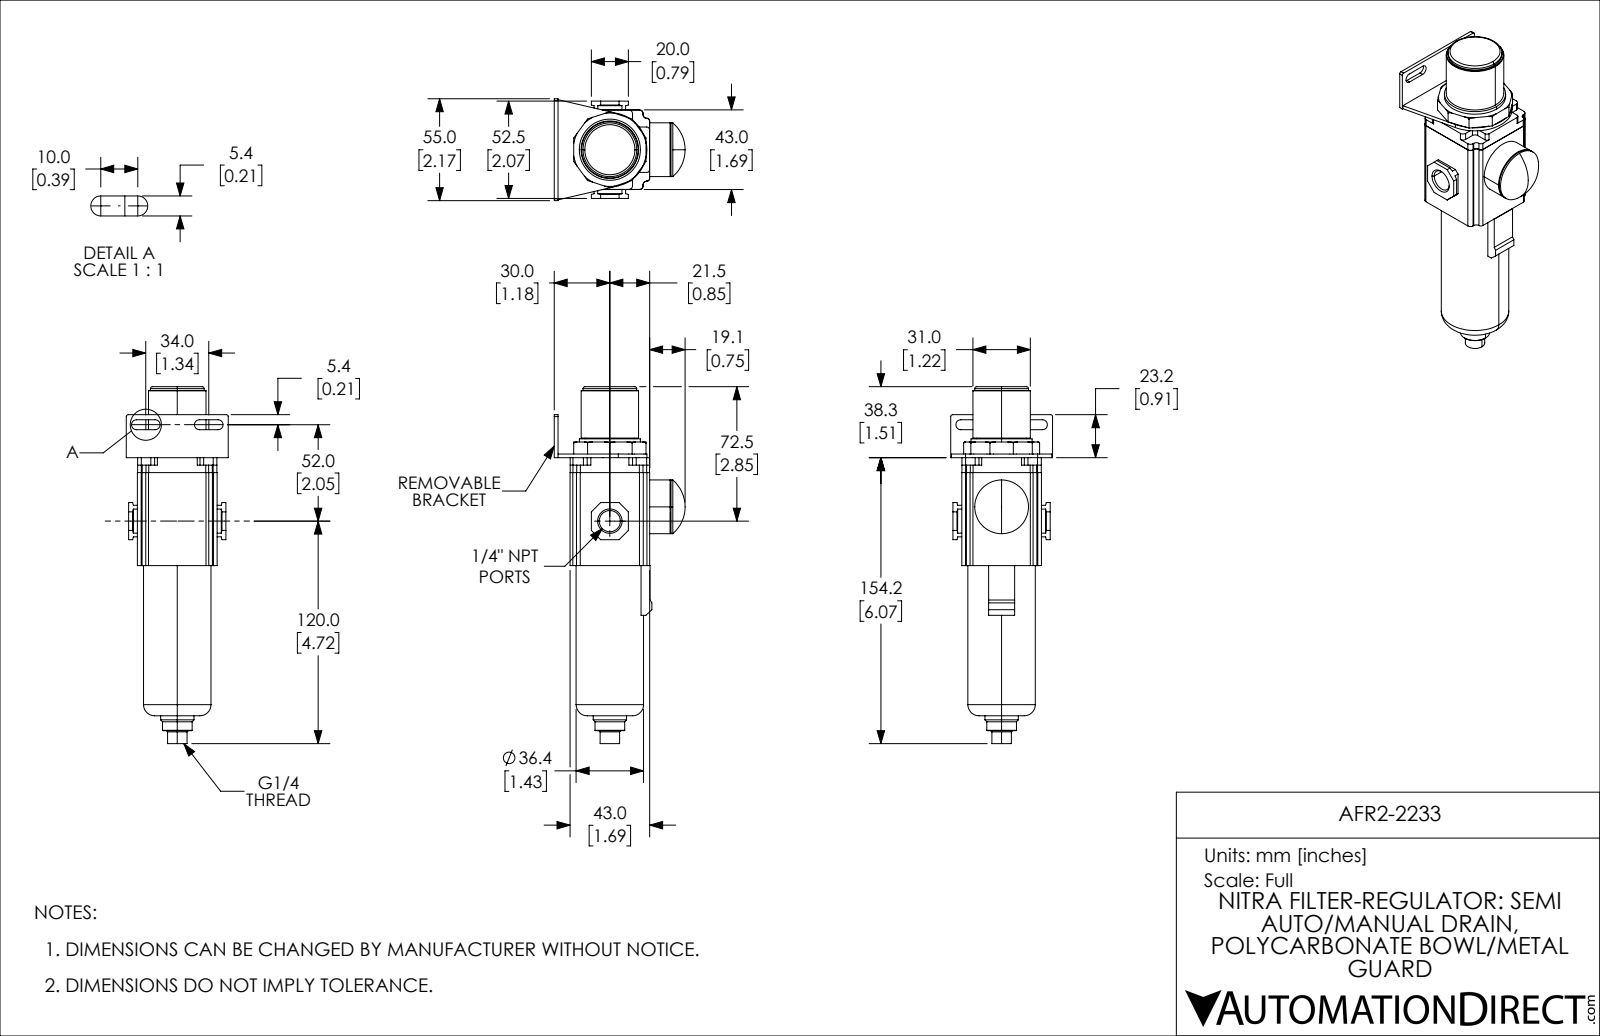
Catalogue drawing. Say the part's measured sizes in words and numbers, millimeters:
The part is named "AFR2-2233". Its 3-D file was written by "SolidWorks 2019 (CONFIG_CONTROL_DESIGN)". It is 1 solid with 220 faces: 119 planar, 69 cylindrical and 32 other. Overall it measures 192.5 by 70.62 by 55 millimeters. Its volume is 237 290 cubic millimeters and its surface area 34 102 square millimeters. Round holes: 1 of diameter 4.13, 1 of diameter 11.45. Round bosses or shafts: 2 of diameter 29, 1 of diameter 36.4, 1 of diameter 33, 1 of diameter 31, 1 of diameter 26.78, 1 of diameter 18, 1 of diameter 16, 1 of diameter 10.5. Partial cylindrical surfaces (rounded edges, fillets, slot ends): 24 of radius 2, 12 of radius 1.5, 4 of radius 2.7, 2 of radius 1, 1 of radius 20. The main face-to-face distances are 43, 2, 8.5, 6.5, 49.5, 51.5, 42.9, 36.3, 58.2, 60.2.
